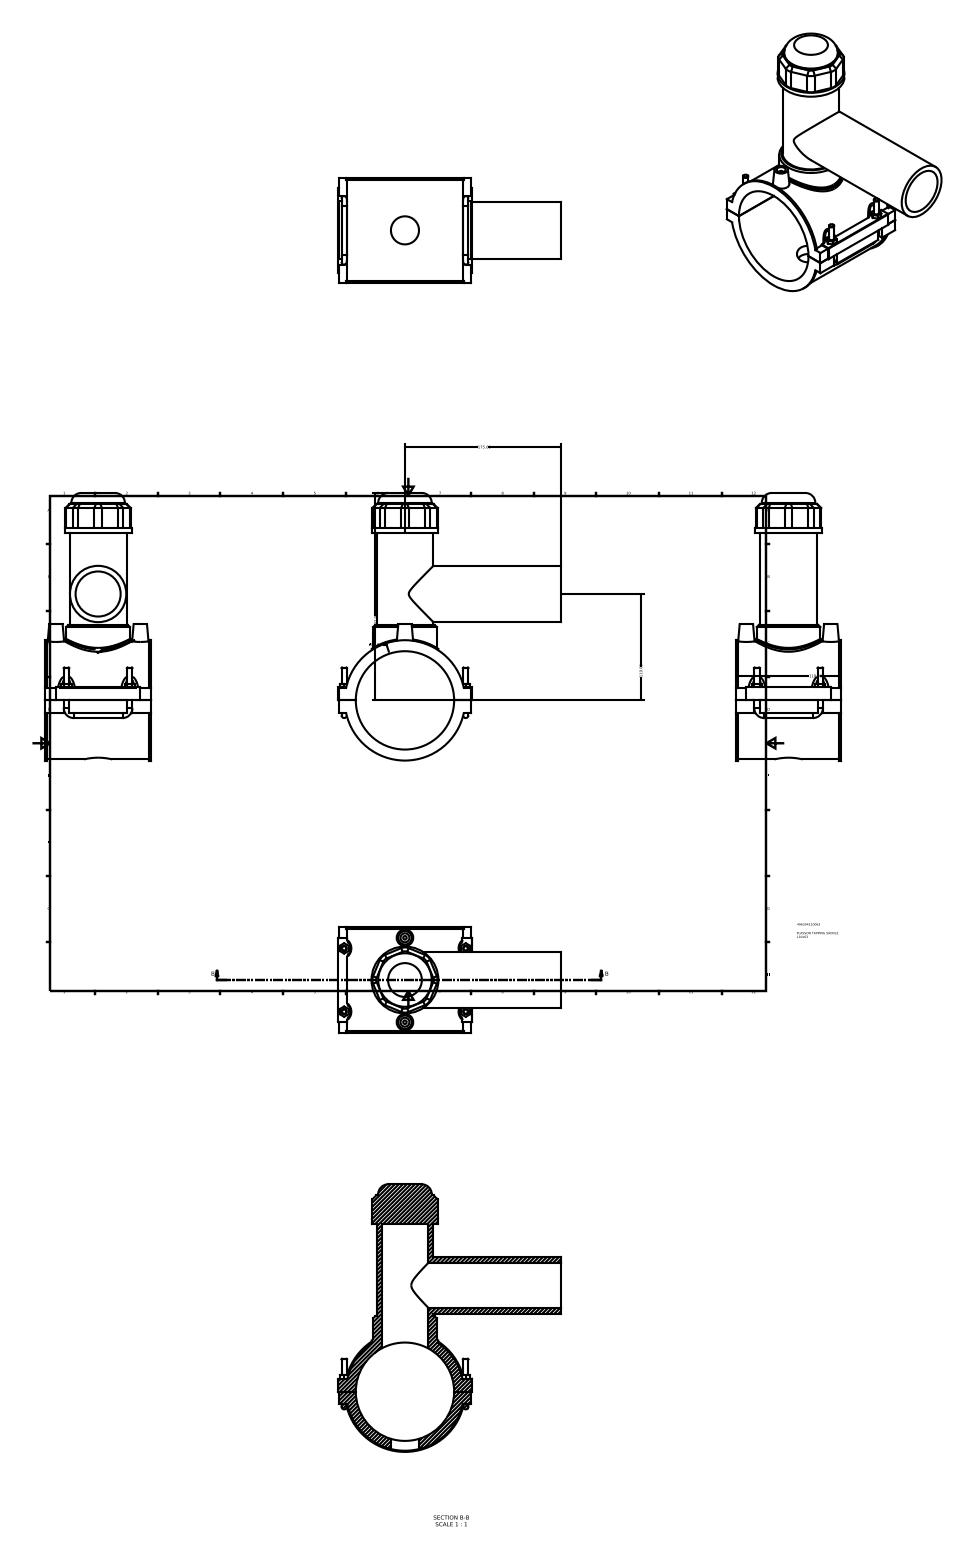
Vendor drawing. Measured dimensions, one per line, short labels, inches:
name: 496304110063
written by: Autodesk Inventor 2015 (AUTOMOTIVE_DESIGN)
unit: in
bodies: 1 solid, 185 faces (111 planar, 49 cylindrical, 25 other)
size: 11.784 × 9.843 × 4.646
volume: 60.61 in³; area: 358.6 in²
holes: 2× ⌀0.394, 1× ⌀1.235, 1× ⌀1.984, 1× ⌀2.061, 1× ⌀4.331
bosses: 6× ⌀0.236, 2× ⌀0.157, 1× ⌀5.301, 1× ⌀5.197, 1× ⌀2.945, 1× ⌀2.798, 1× ⌀2.503, 1× ⌀2.48
rounds: 8× R0.433, 4× R0.118, 4× R0.295, 1× R0.02, 1× R2.702
face distances: 4.646, 7.394, 7.39, 0.039, 5.866, 0.539, 0.543, 7.933, 0.583, 5.827
hole spacings: 1.858, 3.717
